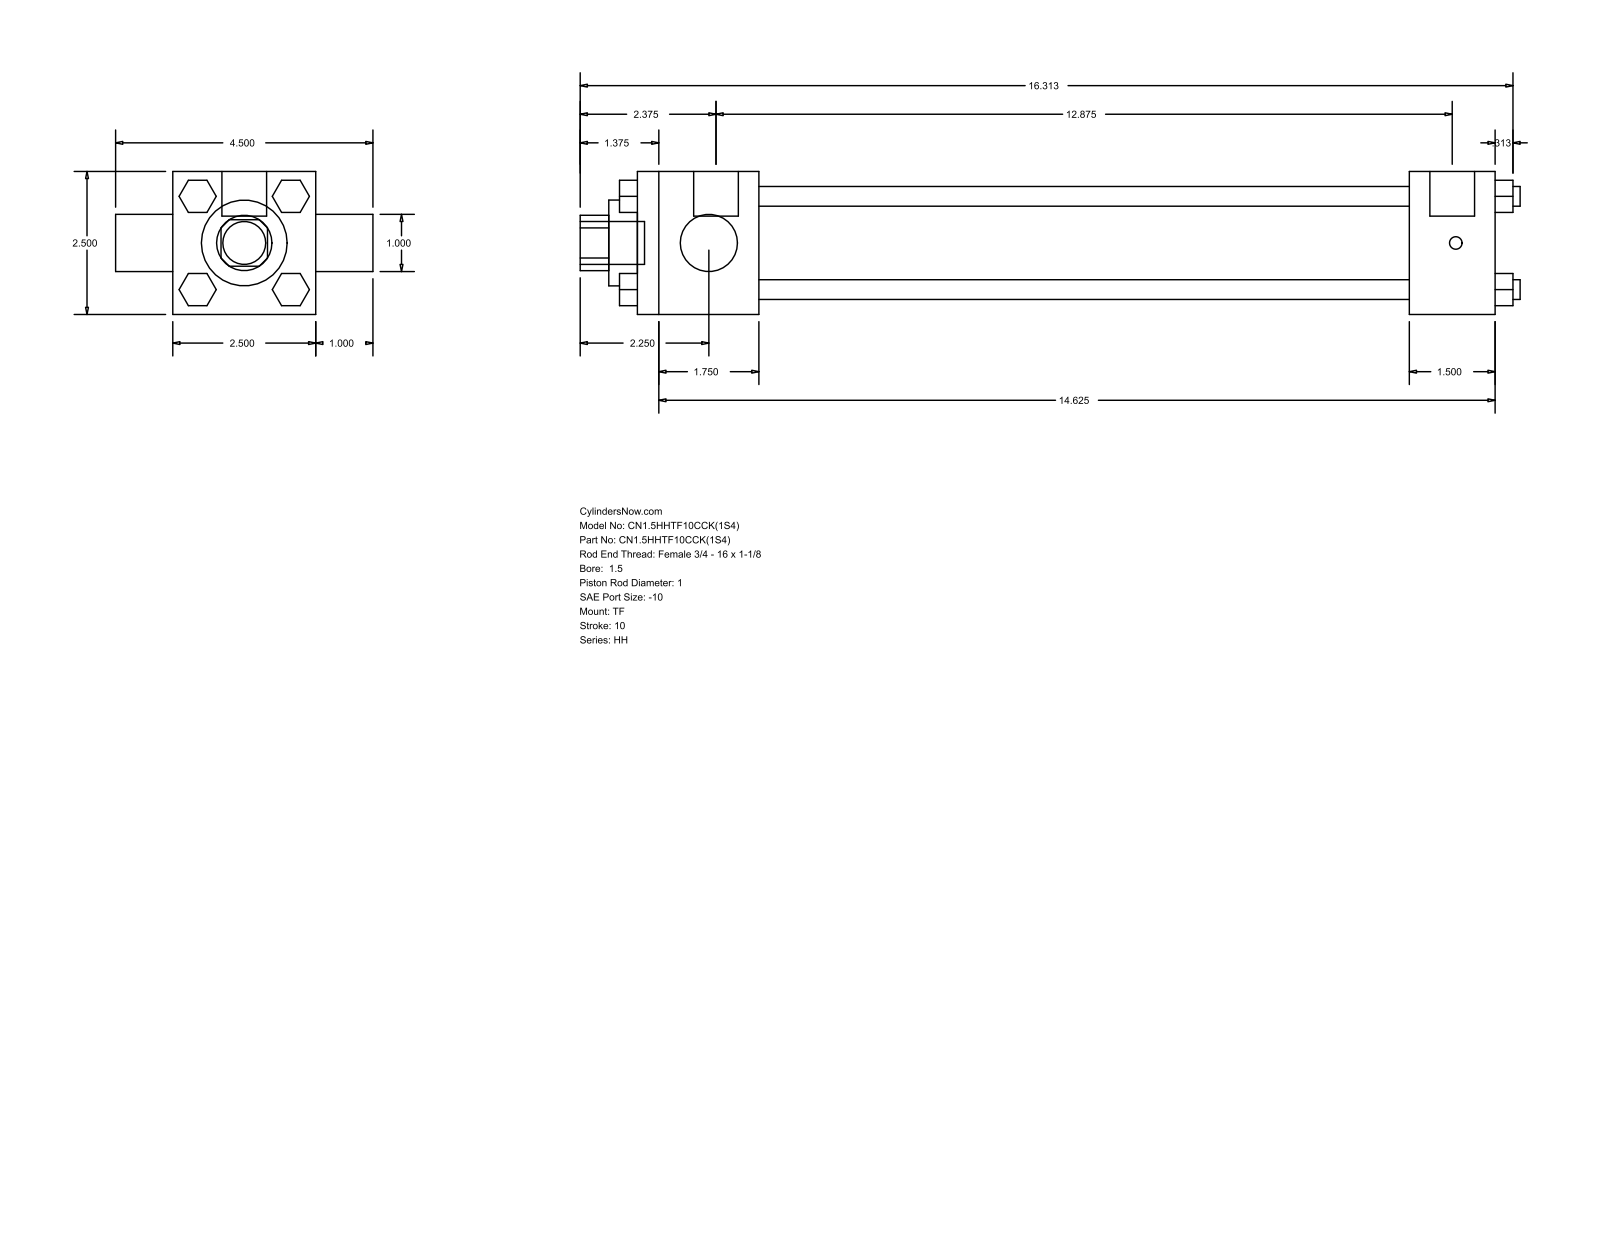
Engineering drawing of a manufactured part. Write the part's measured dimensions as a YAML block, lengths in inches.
part_name: "HH_TF__0150_1"
step_written_by: "GSSL Pune (CONFIG_CONTROL_DESIGN)"
units: inches
bodies: {solids: 0, faces: 120, planar: 92, cylindrical: 28, other: 0}
overall_size: [16.437, 4.5, 2.5]
round_holes:
  - {diameter: 1, count: 2}
  - {diameter: 1.5, count: 1}
  - {diameter: 1.75, count: 1}
round_bosses_or_shafts:
  - {diameter: 0.345, count: 4}
  - {diameter: 0.219, count: 3}
  - {diameter: 0.781, count: 2}
  - {diameter: 0.75, count: 1}
partial_cylinders:
  - {radius: 0.484, count: 1}
face_to_face_distances: [2.5, 12.875, 11.375, 1.5, 2.125, 13.5, 15, 15.313, 1, 0.815]
